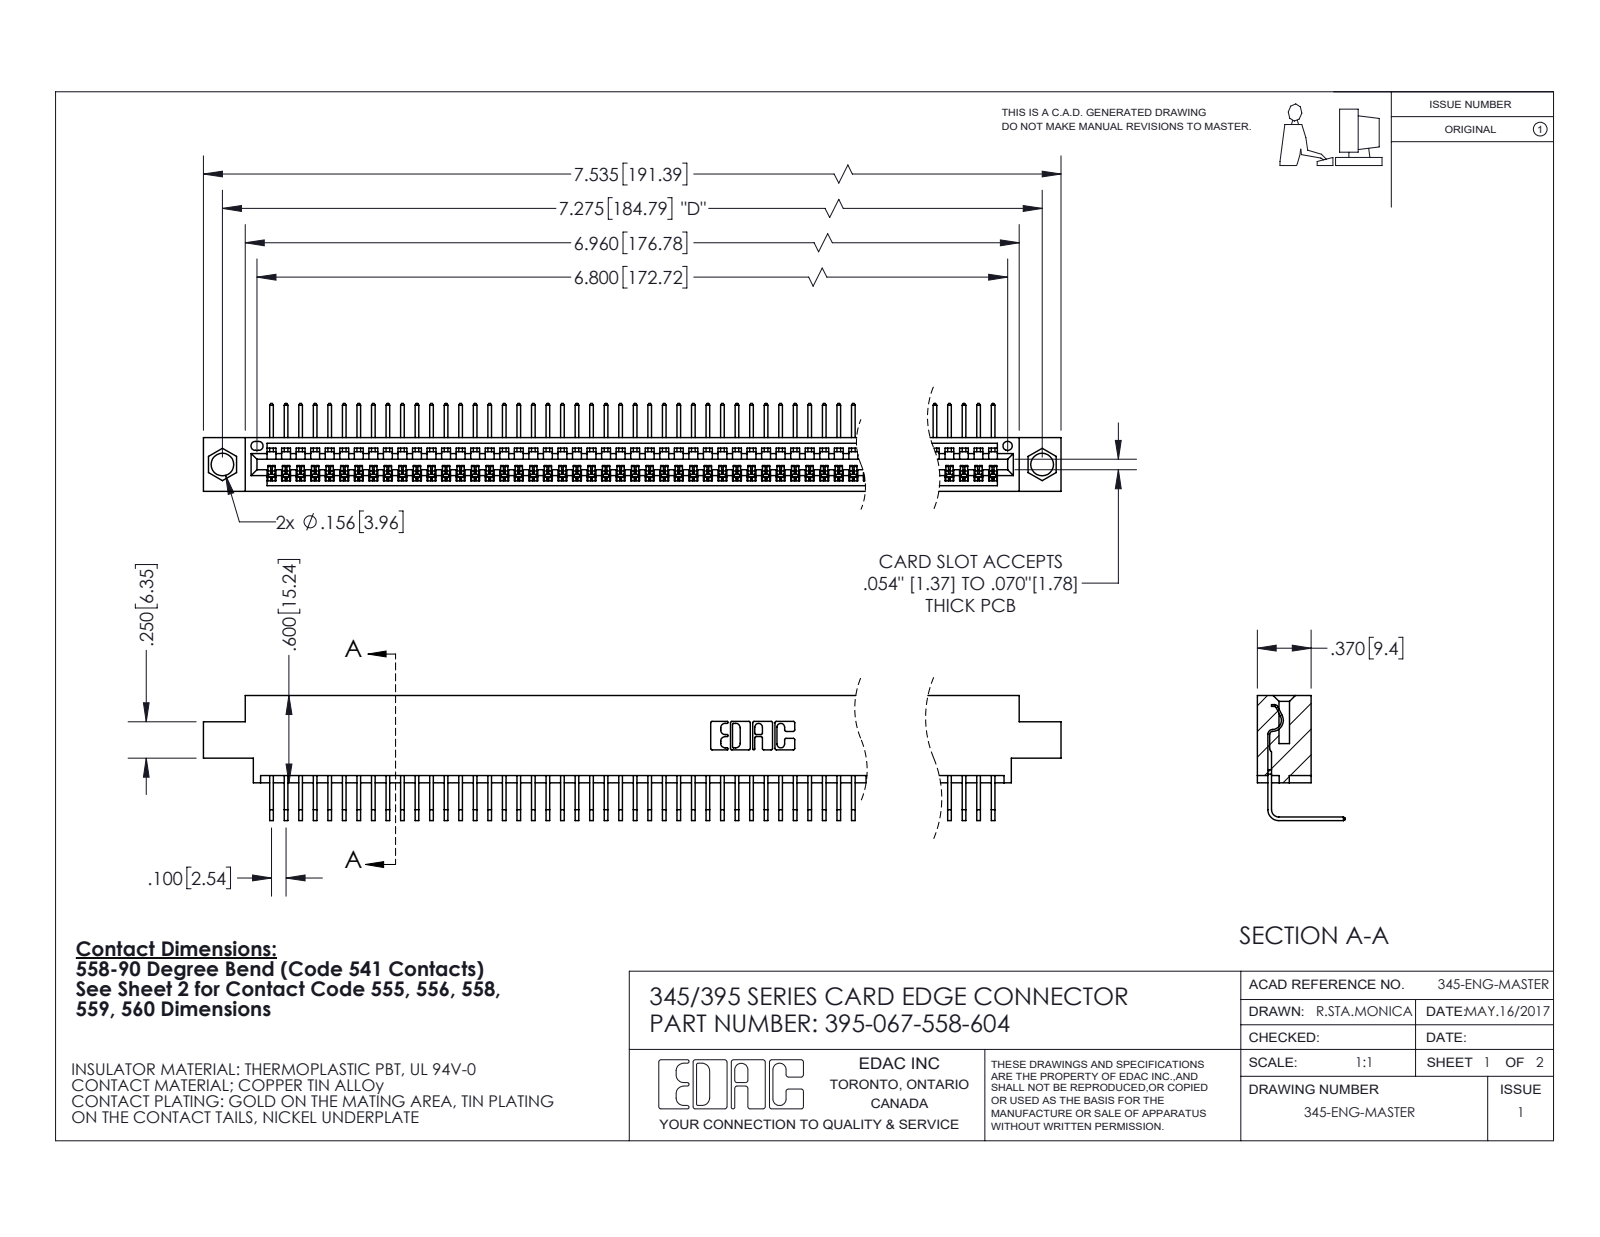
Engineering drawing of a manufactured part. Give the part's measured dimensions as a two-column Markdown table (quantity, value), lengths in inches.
| quantity | value |
| --- | --- |
| part name | 345-292-001_558 Tail - 2; 395-067-558-604; 345 Part_0.170 Offset - 0.156 Dia-TI |
| STEP written by | SolidWorks 2020 (CONFIG_CONTROL_DESIGN) |
| units | inches |
| bodies | 68 solids, 4164 faces (2912 planar, 1252 cylindrical, 0 other) |
| overall size | 7.535 × 0.859 × 0.605 |
| volume | 1.122 in³ |
| surface area | 40.39 in² |
| round holes (diameter × count) | 0.156 × 2, 0.064 × 1 |
| partial cylindrical surfaces (radius × count) | 0.006 × 134, 0.01 × 22, 0.007 × 6, 0.031 × 6, 0.026 × 3, 0.031 × 2, 0.04 × 2, 0.014 × 1 |
| main face-to-face distances | 0.072, 0.298, 0.37, 0.2, 0.098, 0.272, 0.025, 0.225, 0.175, 0.149 |
| hole center spacings | 0.27, 7.039, 7.275 |
